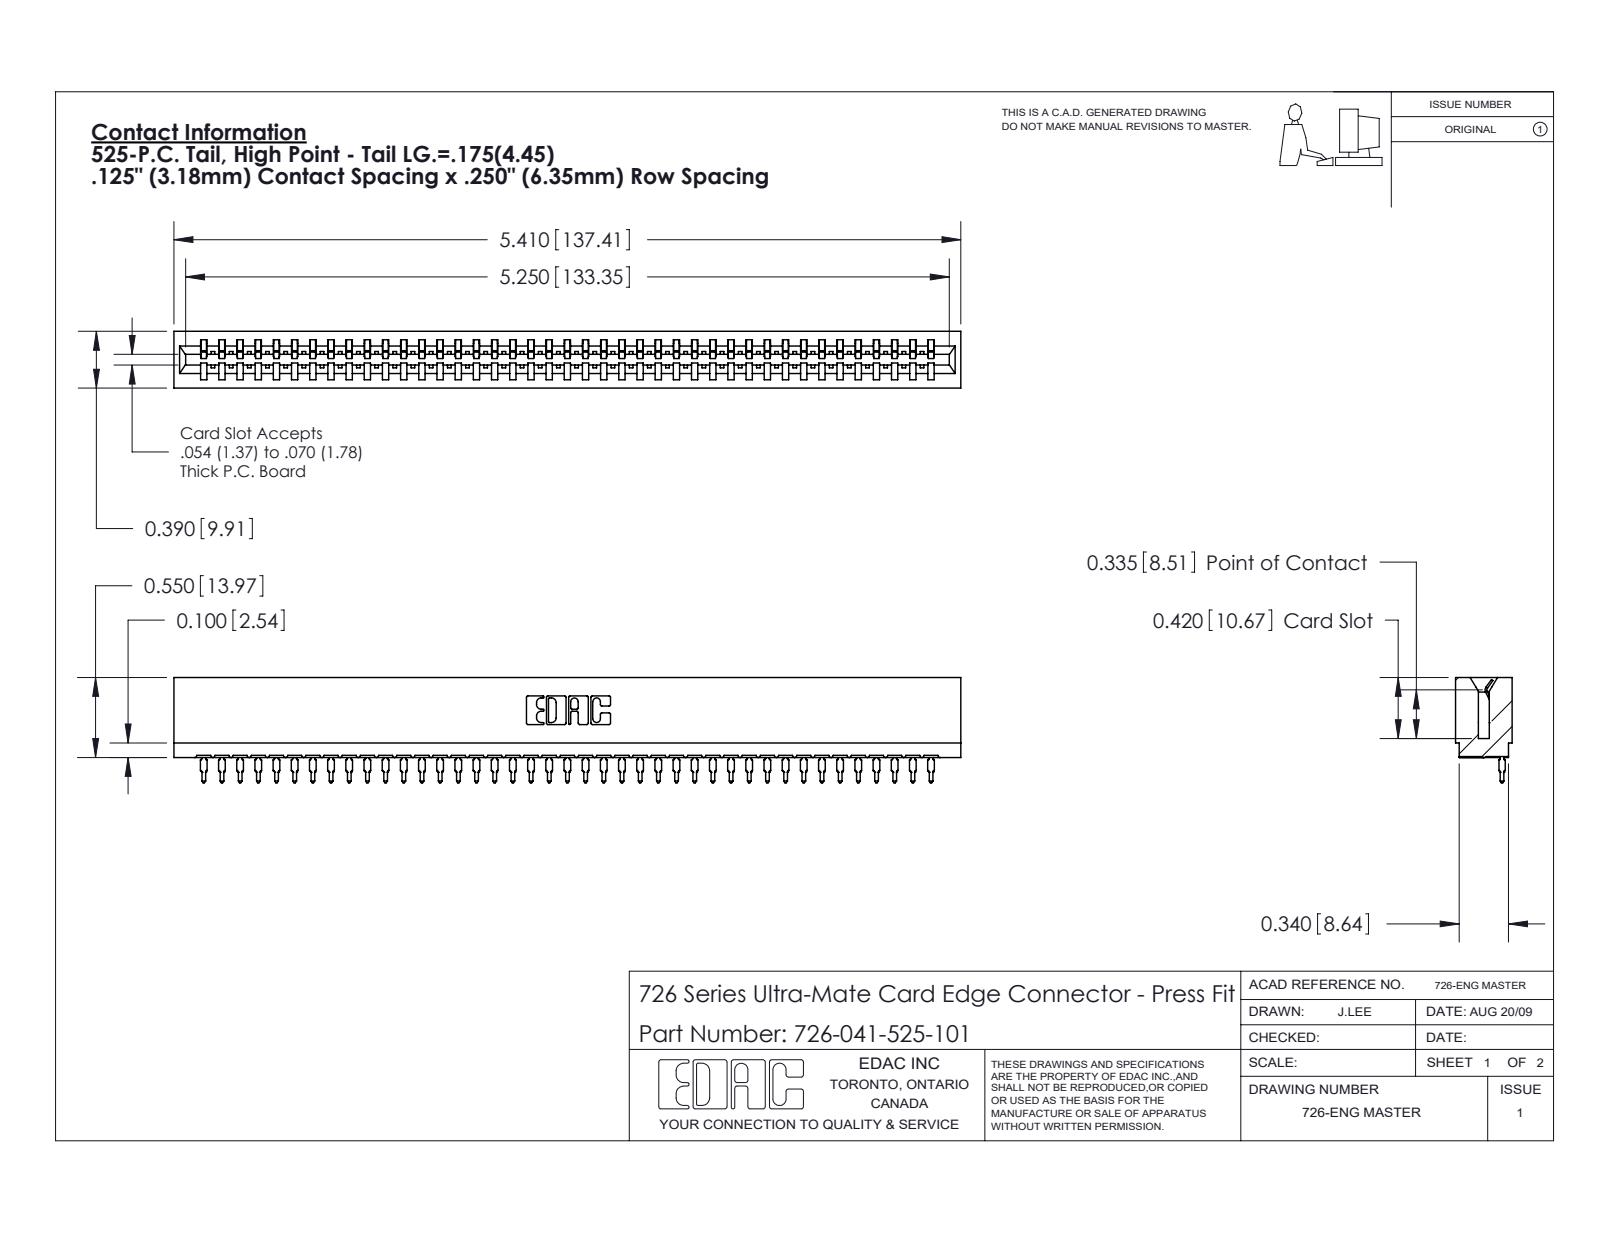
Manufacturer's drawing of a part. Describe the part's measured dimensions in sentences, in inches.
The part is named "726-041-525-101; 726 Part_.515 Slot Depth - 01; 746-292-001_525". Its 3-D file was written by "SolidWorks 2020 (CONFIG_CONTROL_DESIGN)". It is 42 solids with 4525 faces: 2638 planar, 821 cylindrical and 1066 other. Overall it measures 5.41 by 0.724 by 0.39 inches. Its volume is 0.746 cubic inches and its surface area 28.59 square inches. Partial cylindrical surfaces (rounded edges, fillets, slot ends): 82 of radius 0.021, 42 of radius 0.015, 22 of radius 0.01, 6 of radius 0.007, 6 of radius 0.031, 4 of radius 0.005, 4 of radius 0.011, 3 of radius 0.026. The main face-to-face distances are 0.057, 0.333, 0.39, 0.025, 0.307, 0.25, 0.275, 0.365, 0.032, 0.174.
